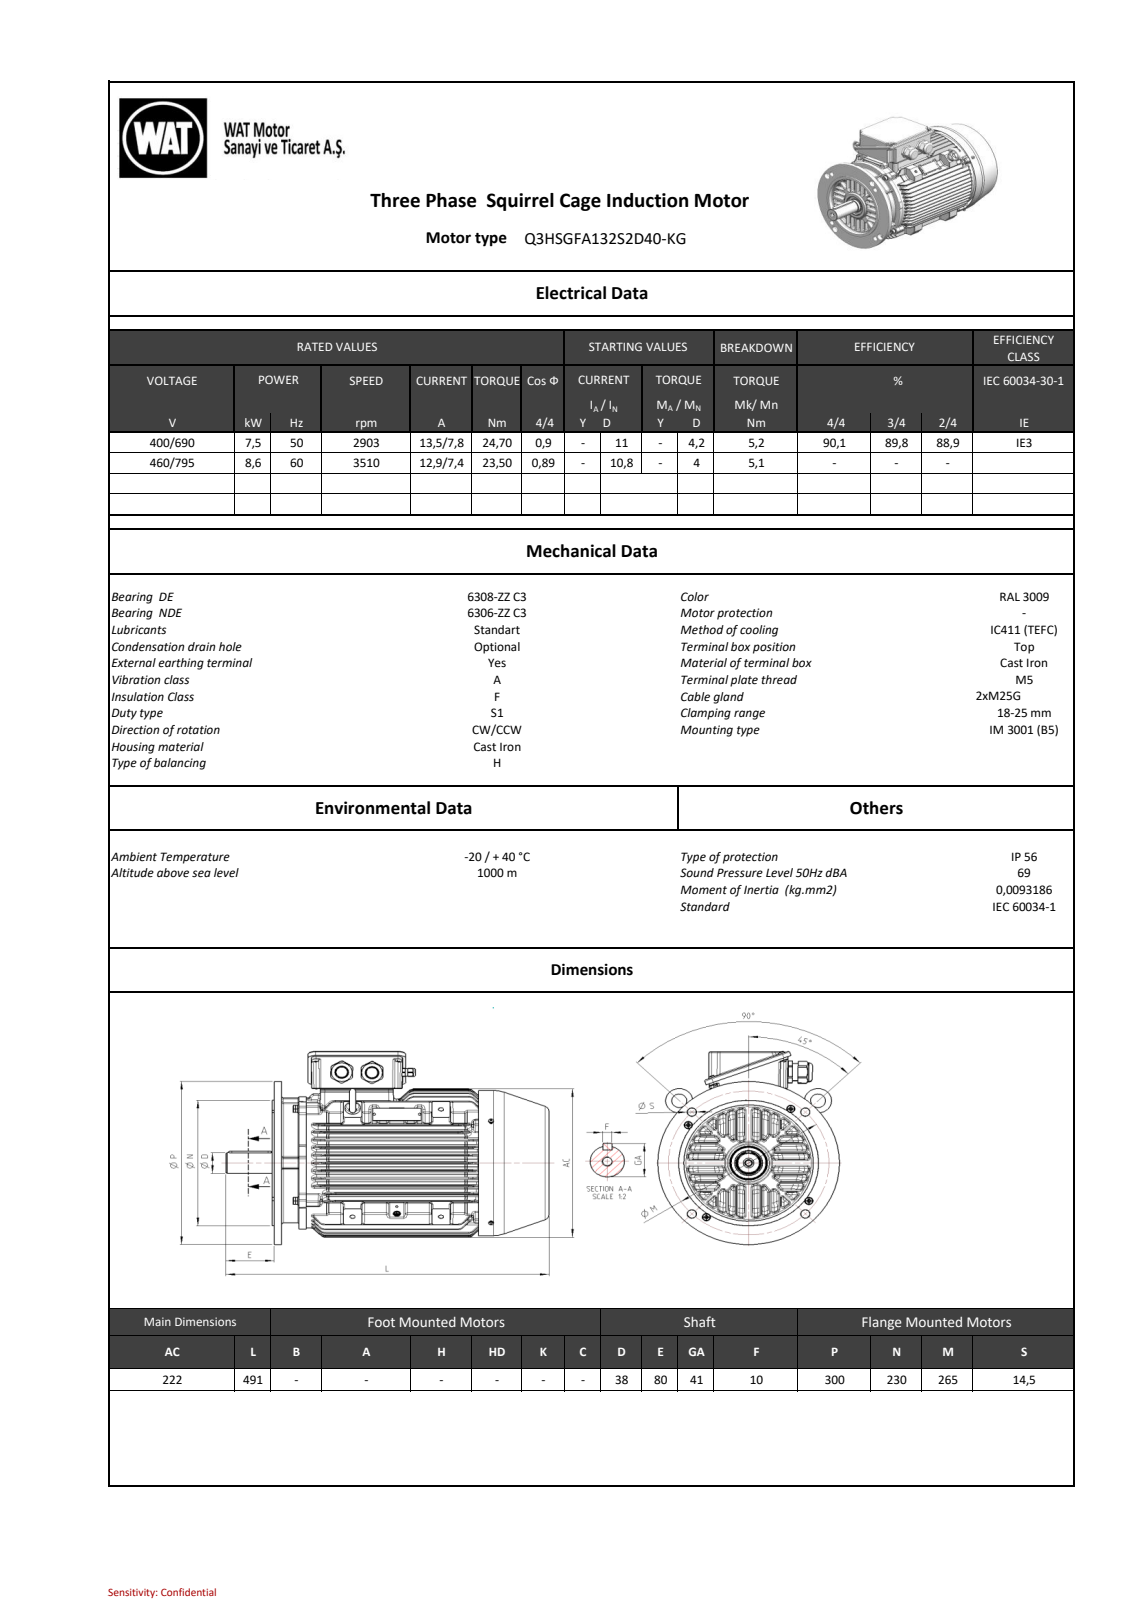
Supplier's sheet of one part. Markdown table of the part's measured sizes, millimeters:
| quantity | value |
| --- | --- |
| part name | 260021E4F5C7p853 |
| STEP written by | SIEMENS PLM Software NX 11.0 (AUTOMOTIVE_DESIGN) |
| units | millimeters |
| bodies | 0 solids, 4193 faces (864 planar, 1180 cylindrical, 2149 other) |
| overall size | 491 × 328.63 × 299 |
| round holes (diameter × count) | 5 × 8, 6.8 × 6, 10 × 4, 12 × 4, 2.5 × 2, 17.2 × 2, 6 × 1, 6.3 × 1, 8 × 1, 10.2 × 1, 11.3 × 1, 13 × 1 |
| round bosses / shafts (diameter × count) | 8.65 × 4, 8 × 4, 4 × 3, 27.7 × 2, 25.25 × 2, 20 × 2, 12 × 2, 299 × 1 |
| partial cylindrical surfaces (radius × count) | 4 × 275, 1.5 × 96, 3 × 81, 0.5 × 77, 2 × 44, 1.8 × 24, 1 × 23, 0.25 × 17 |
| main face-to-face distances | 6, 51, 13.1, 26.28, 13.18, 39.54, 26.44, 13.26, 39.96, 90.54 |
| hole center spacings | 65.3, 97, 137.18, 33.69, 38.02, 111.28, 130, 158.92 |
